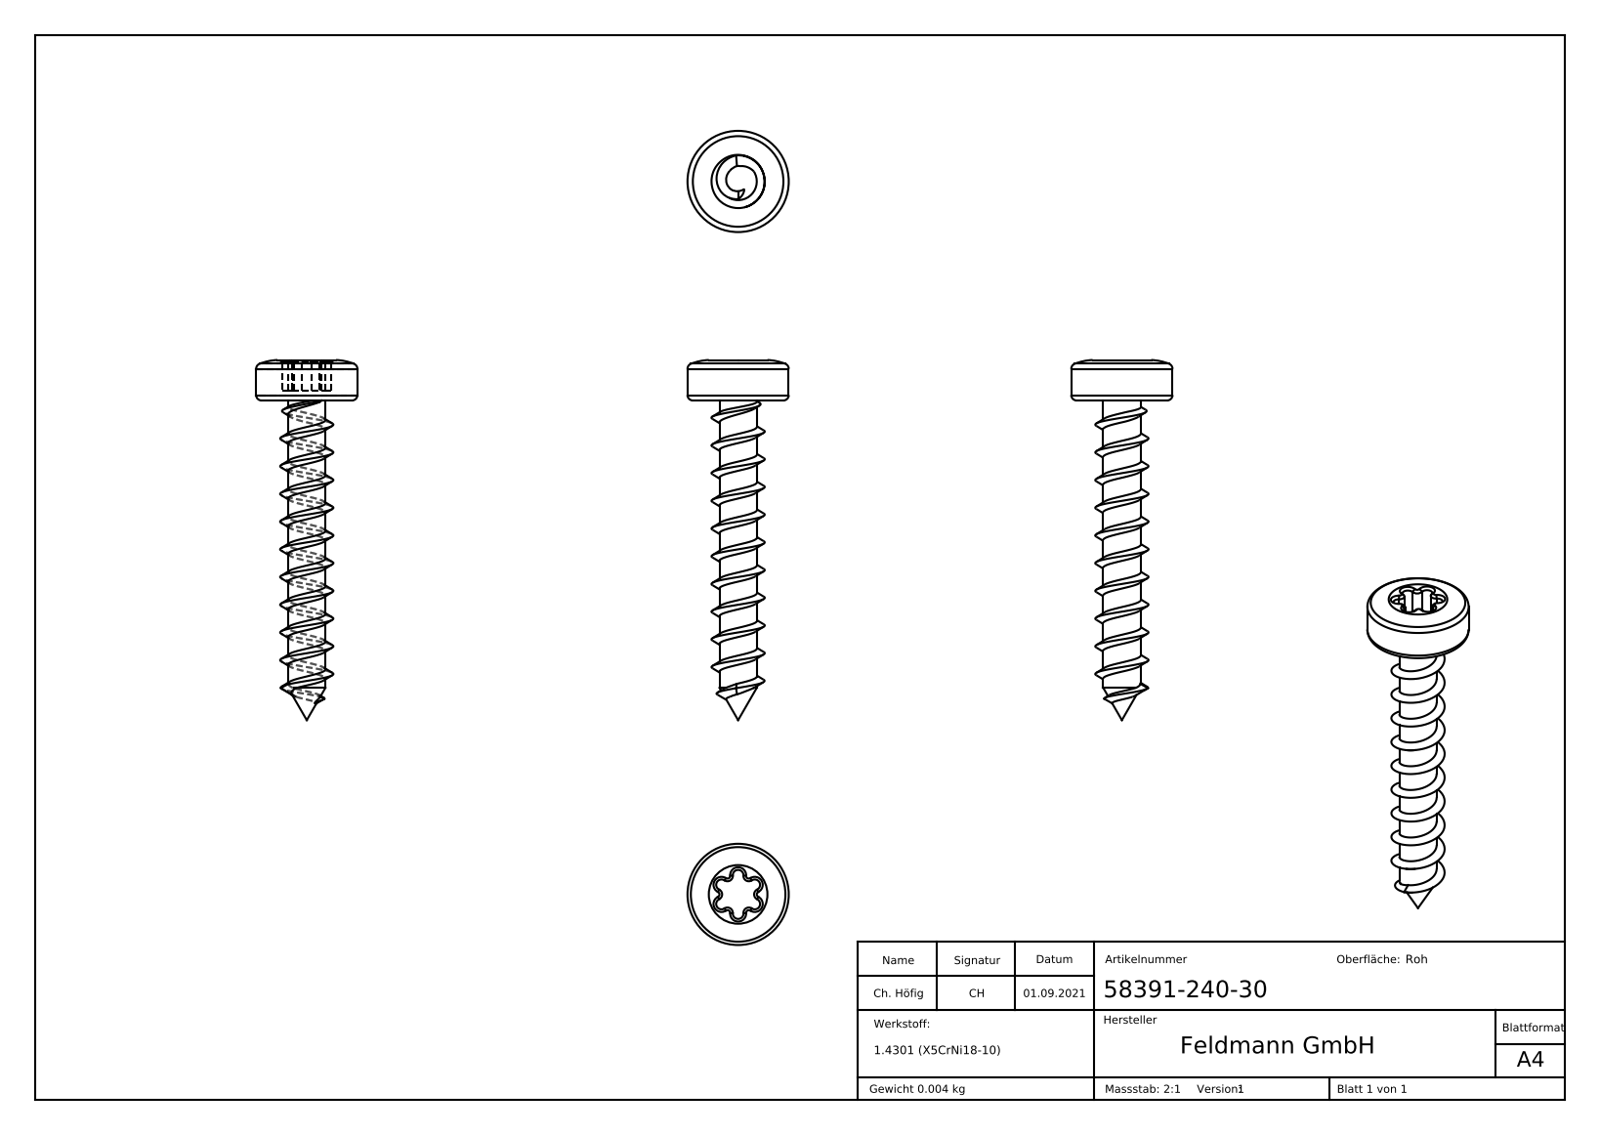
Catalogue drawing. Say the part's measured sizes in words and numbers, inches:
The part is named "58391-240-30". Its 3-D file was written by "SolidWorks 2018 (CONFIG_CONTROL_DESIGN)". It is 1 solid with 42 faces: 4 planar, 14 cylindrical and 24 other. Overall it measures 1.275 by 0.374 by 0.374 inches. Its volume is 0.031 cubic inches and its surface area 1.13 square inches. Round bosses or shafts: 1 of diameter 0.374, 1 of diameter 0.138. Partial cylindrical surfaces (rounded edges, fillets, slot ends): 6 of radius 0.02, 6 of radius 0.02. The main face-to-face distances are 0.035, 0.114, 0.15.
